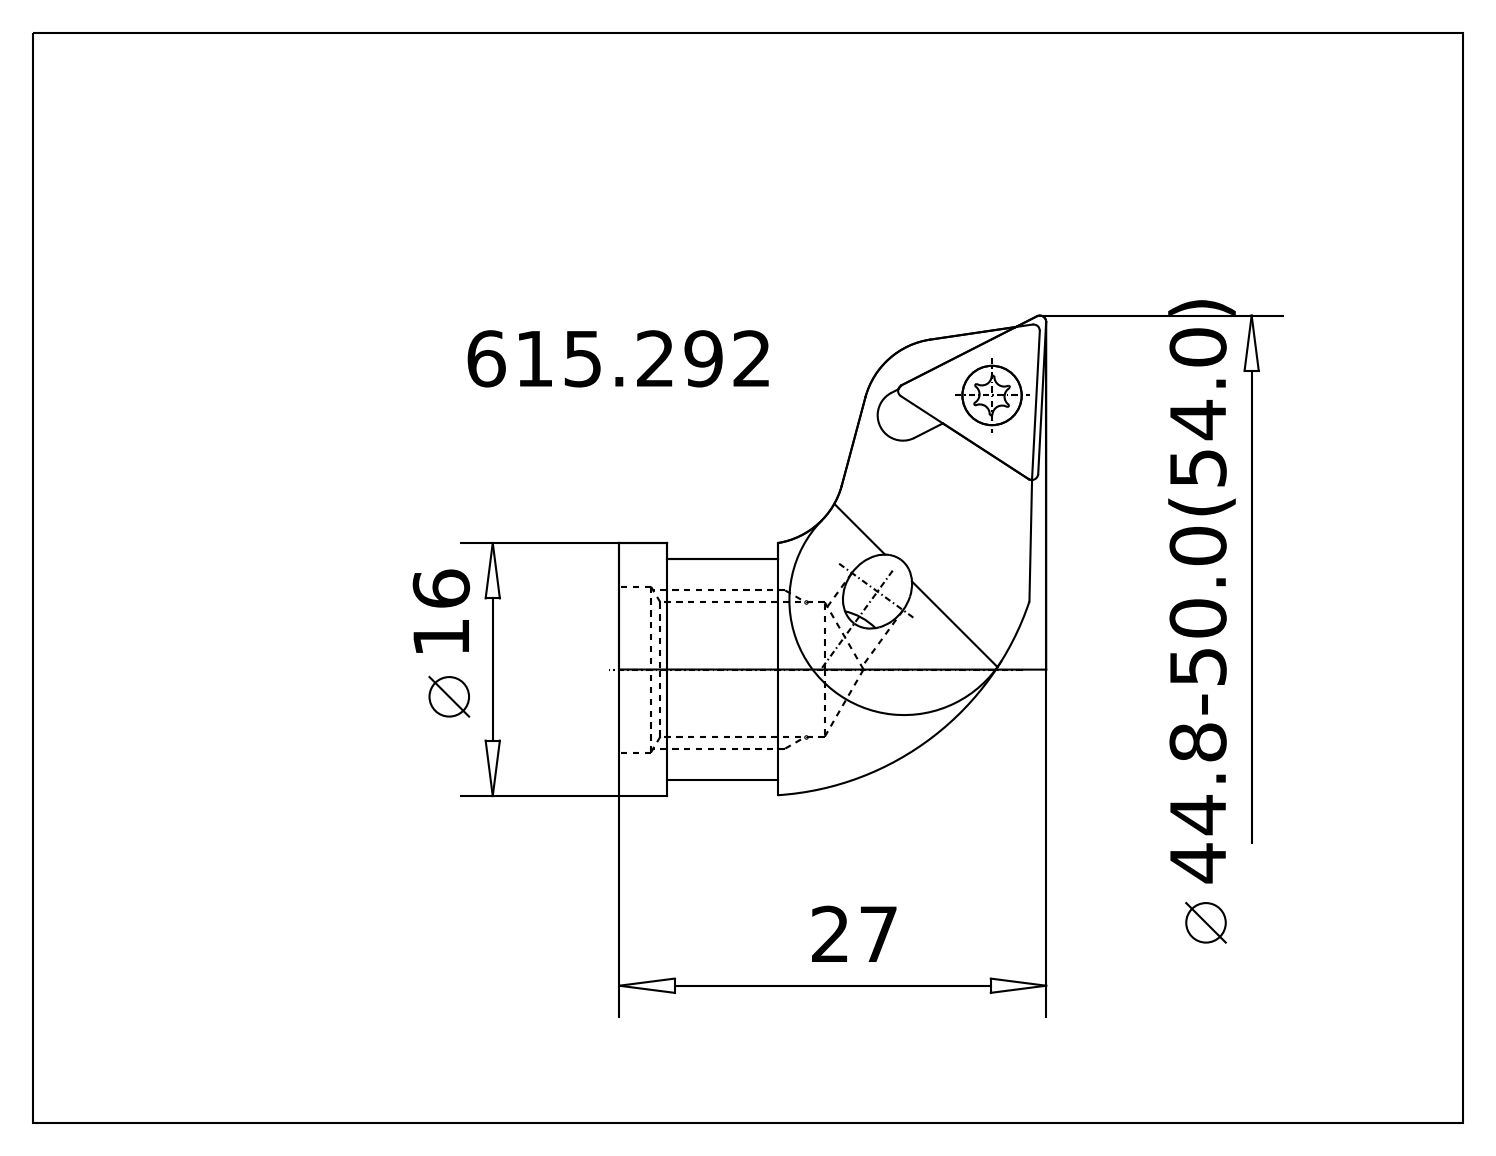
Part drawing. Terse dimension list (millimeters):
name: 615.292 Kaiser E45 TC11|655.383 Kaiser TCGT 110204 K10C;Kombinieren1; 615.292 Kaiser E45 TC11|694.122 Kaiser ETL M2.5x6.5 T7 IP 10S;Kreismuster1; 615.292 Kaiser E45 TC11|615.292 Kaiser E45 TC11;Schnitt-Rotation2
written by: ACIS (automotive_design)
unit: mm
bodies: 3 solids, 131 faces (30 planar, 52 cylindrical, 49 other)
size: 30.4 × 27 × 16
volume: 4 252 mm³; area: 2 641 mm²
holes: 1× ⌀2, 1× ⌀2.8, 1× ⌀4, 1× ⌀8.5, 1× ⌀10
bosses: 1× ⌀16, 1× ⌀3.45, 1× ⌀2.5
rounds: 6× R0.15, 6× R0.4, 4× R0.2, 2× R3, 1× R1.6, 1× R6, 1× R7.8
face distances: 7.7, 5.6, 2.1, 14, 7.98, 2.38, 11, 11.01, 1.01, 1
